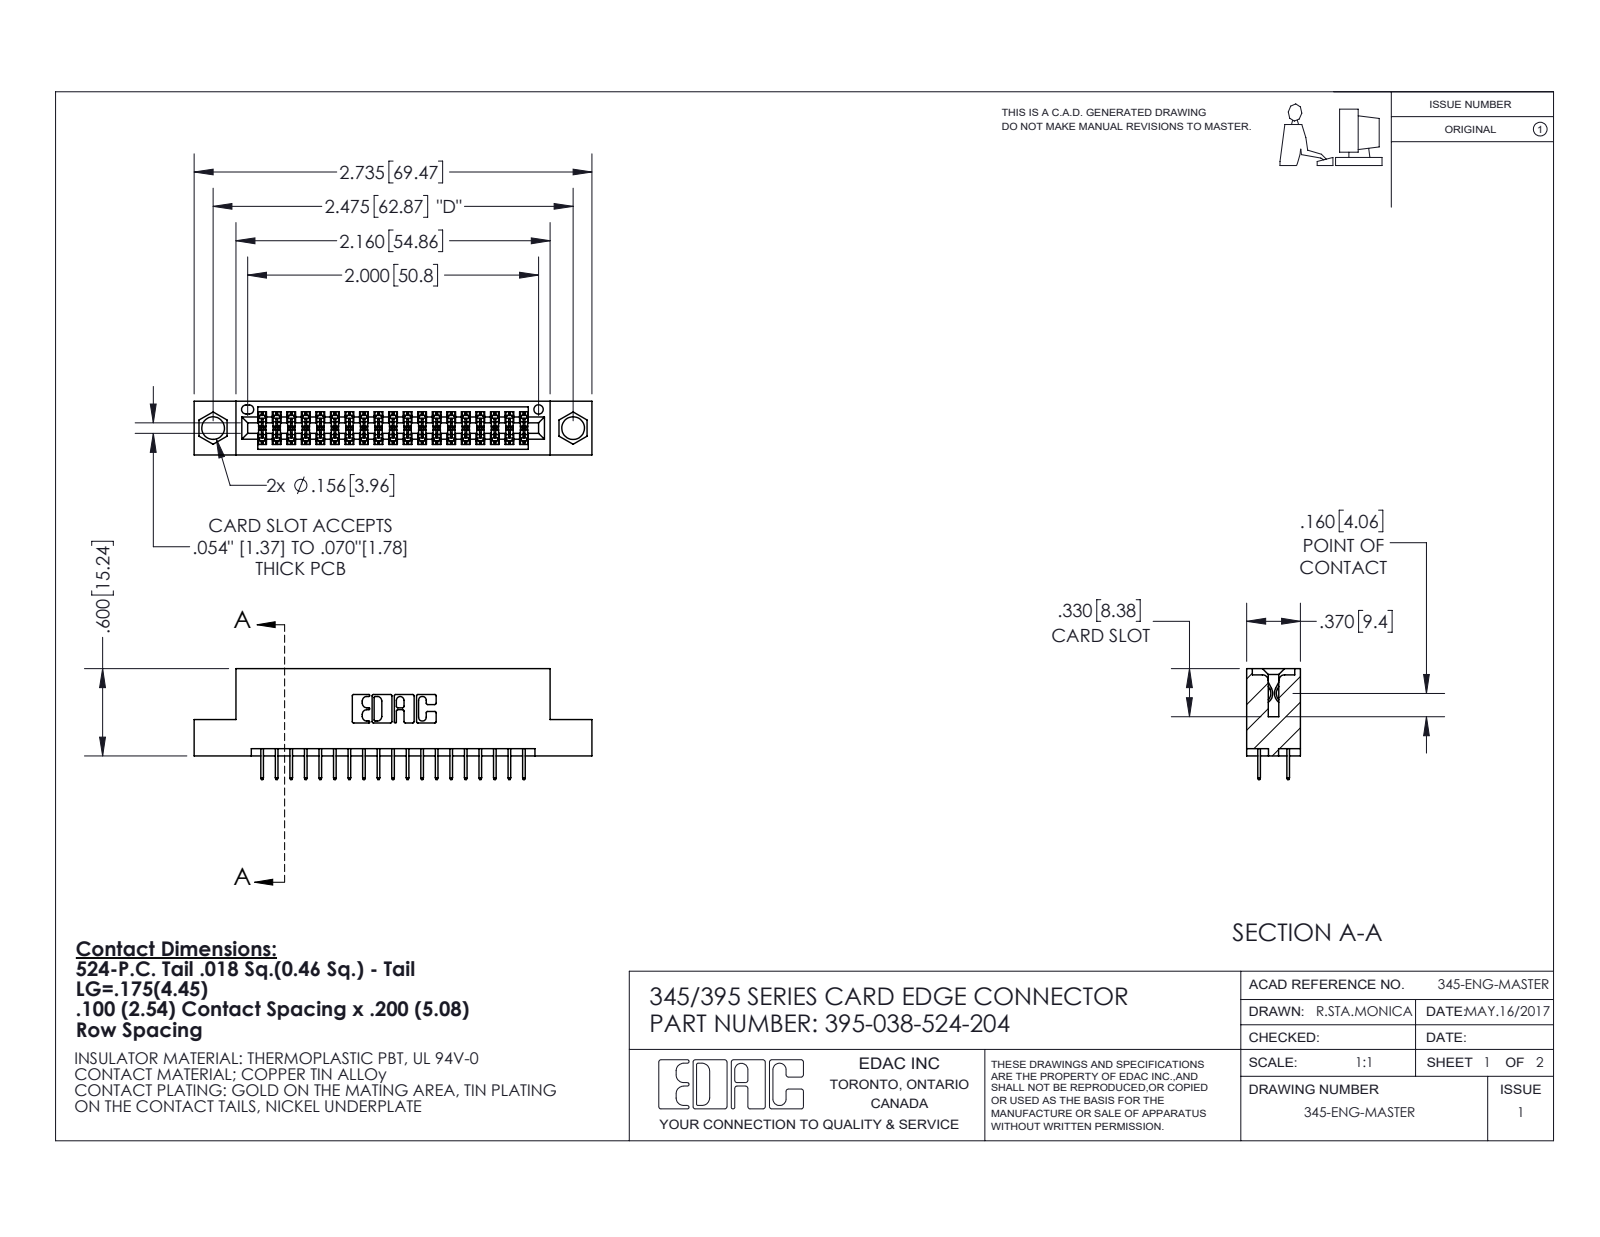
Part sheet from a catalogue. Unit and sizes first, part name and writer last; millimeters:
Units: millimetres
Overall size (bounding box): 69.5 × 19.4 × 9.4
Round holes (diameter × count): ⌀4 ×2, ⌀1.6 ×1
Partial cylindrical surfaces — rounded edges, fillets, slot ends (radius × count): R0.2 ×58, R0.3 ×22, R0.2 ×6, R0.8 ×6, R0.7 ×3, R0.4 ×2, R0.5 ×2, R0.6 ×2
Main face-to-face distances: 1.8, 7.6, 5.1, 9.4, 2.5, 6.9, 0.6, 5.7, 1.8, 4.4
Hole centre spacings: 6.9, 56.9, 62.9
Volume: 6 370 mm³ · Surface area: 8 671 mm²
Bodies: 39 solids, 2192 faces (1576 planar, 616 cylindrical, 0 other)
Part name (STEP PRODUCT): 395-038-524-204; 345-292-001_345-293-124; 345 Part_Flush Mounting Lugs - 0.156 Dia-TI
STEP written by: SolidWorks 2020 (CONFIG_CONTROL_DESIGN)
